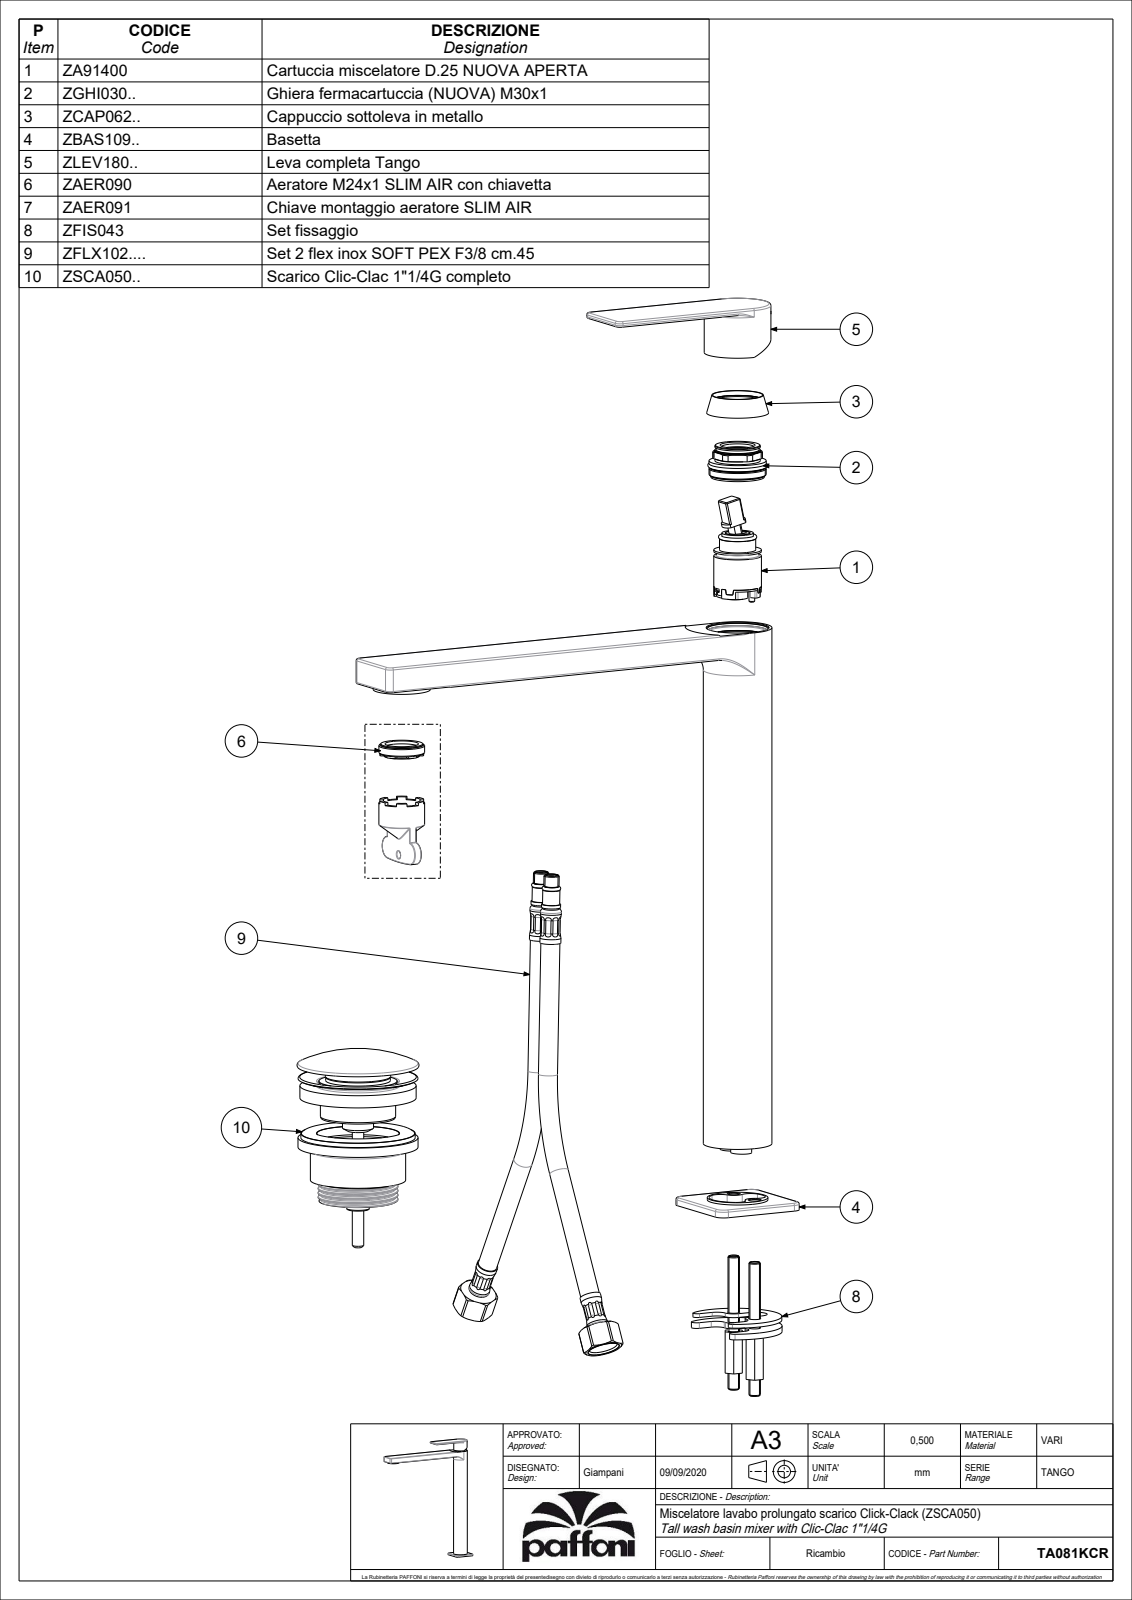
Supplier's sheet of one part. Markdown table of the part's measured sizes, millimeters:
| quantity | value |
| --- | --- |
| part name | TA081CR |
| STEP written by | CREO PARAMETRIC BY PTC INC, 2020044 (CONFIG_CONTROL_DESIGN) |
| units | millimeters |
| bodies | 0 solids, 79 faces (19 planar, 32 cylindrical, 28 other) |
| overall size | 307.7 × 247 × 50 |
| round bosses / shafts (diameter × count) | 36 × 1, 35 × 1, 30 × 1 |
| partial cylindrical surfaces (radius × count) | 1 × 16, 3 × 4, 5 × 4, 0.8 × 2 |
| main face-to-face distances | 13.5, 41.2, 27.7, 36, 266, 279.5, 307.2, 4, 262, 275.5 |
